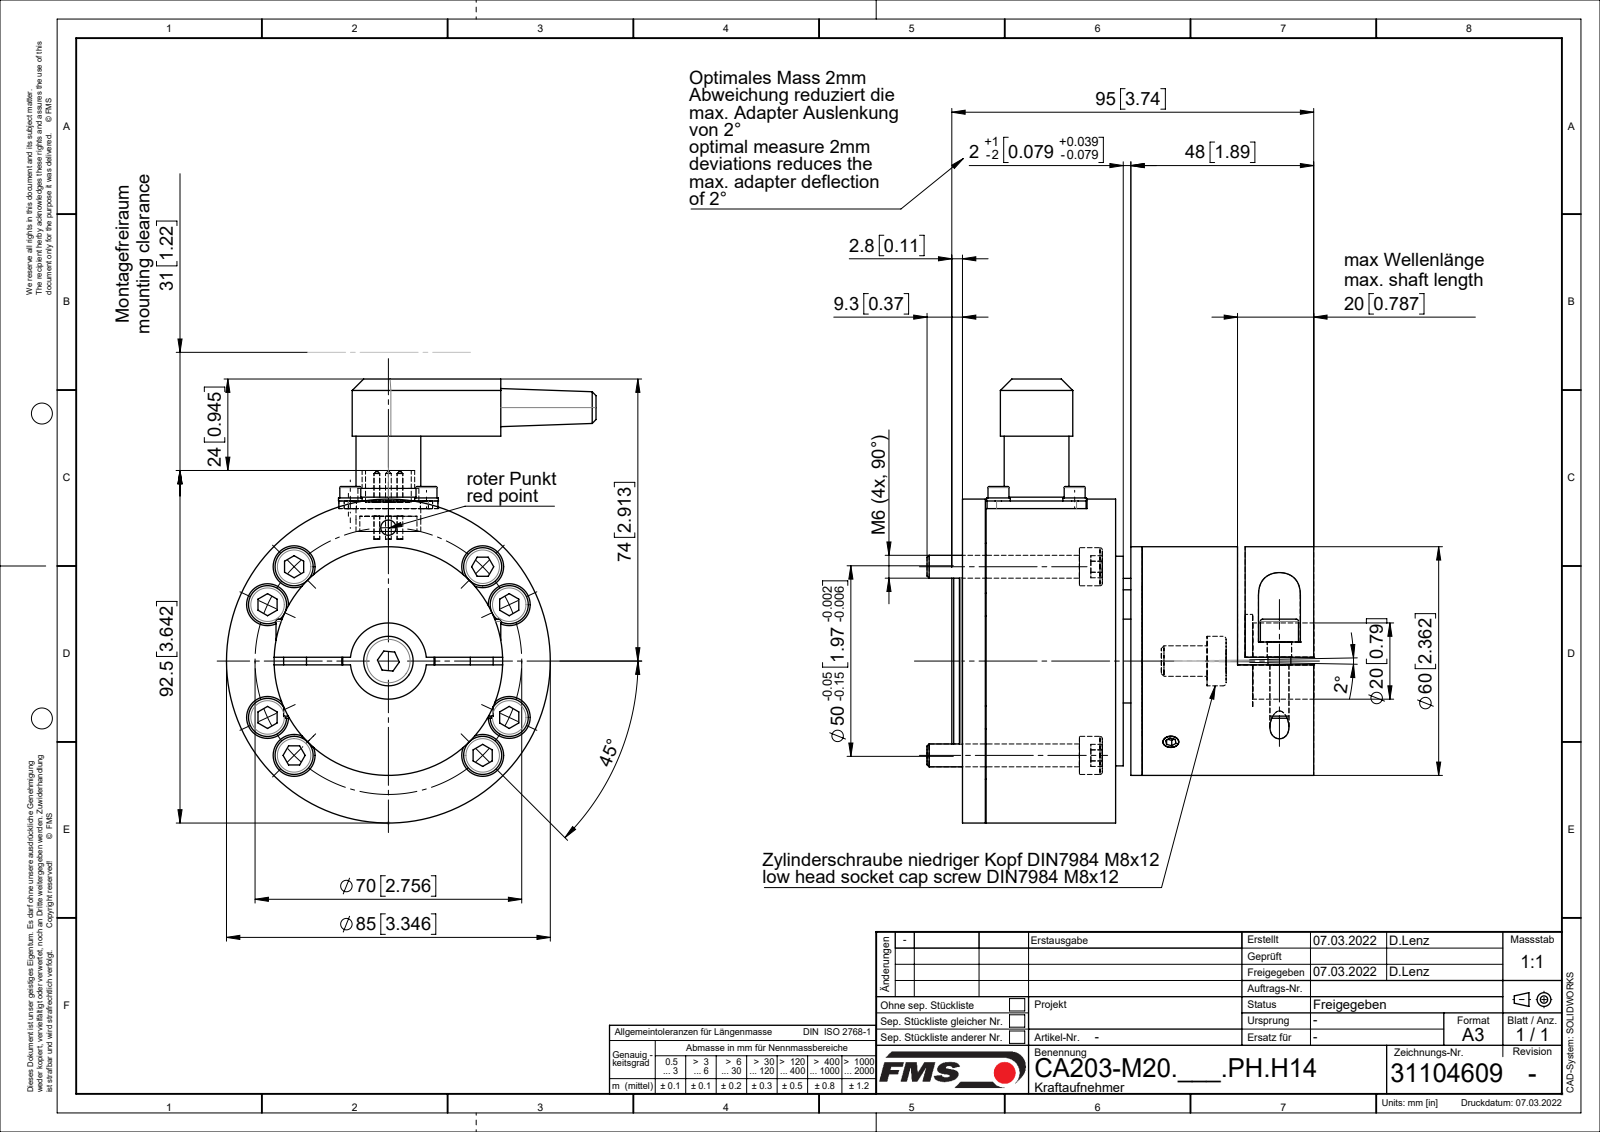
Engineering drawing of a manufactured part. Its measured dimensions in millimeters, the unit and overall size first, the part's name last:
Units: millimetres
Overall size (bounding box): 116.5 × 101.5 × 97
Round holes (diameter × count): ⌀2.5 ×8, ⌀6.5 ×8, ⌀11 ×8, ⌀5 ×6, ⌀2 ×5, ⌀4 ×5, ⌀3.1 ×4, ⌀3.2 ×4, ⌀3.6 ×4, ⌀7 ×4, ⌀6.4 ×2, ⌀3 ×1
Round bosses / shafts (diameter × count): ⌀6 ×11, ⌀10 ×10, ⌀3 ×8, ⌀1.5 ×5, ⌀6.2 ×4, ⌀5.7 ×4, ⌀5.5 ×4, ⌀85 ×1
Partial cylindrical surfaces — rounded edges, fillets, slot ends (radius × count): R2.5 ×4, R5 ×2, R5.5 ×2, R9.5 ×1
Main face-to-face distances: 2, 41, 30, 45, 6, 34, 10, 3, 50, 12
Hole centre spacings: 35, 20, 24.78, 25.2, 32.8, 51.14, 56.46, 6
Volume: 307 921 mm³ · Surface area: 112 111 mm²
Bodies: 44 solids, 846 faces (304 planar, 344 cylindrical, 198 other)
Part name (STEP PRODUCT): Sch DIN9021_M8; 070907-2_01; 091113-3_stp_01; Zyl-Schr DIN912_M6x40 (+8 more)
STEP written by: SolidWorks 2018 (CONFIG_CONTROL_DESIGN)
